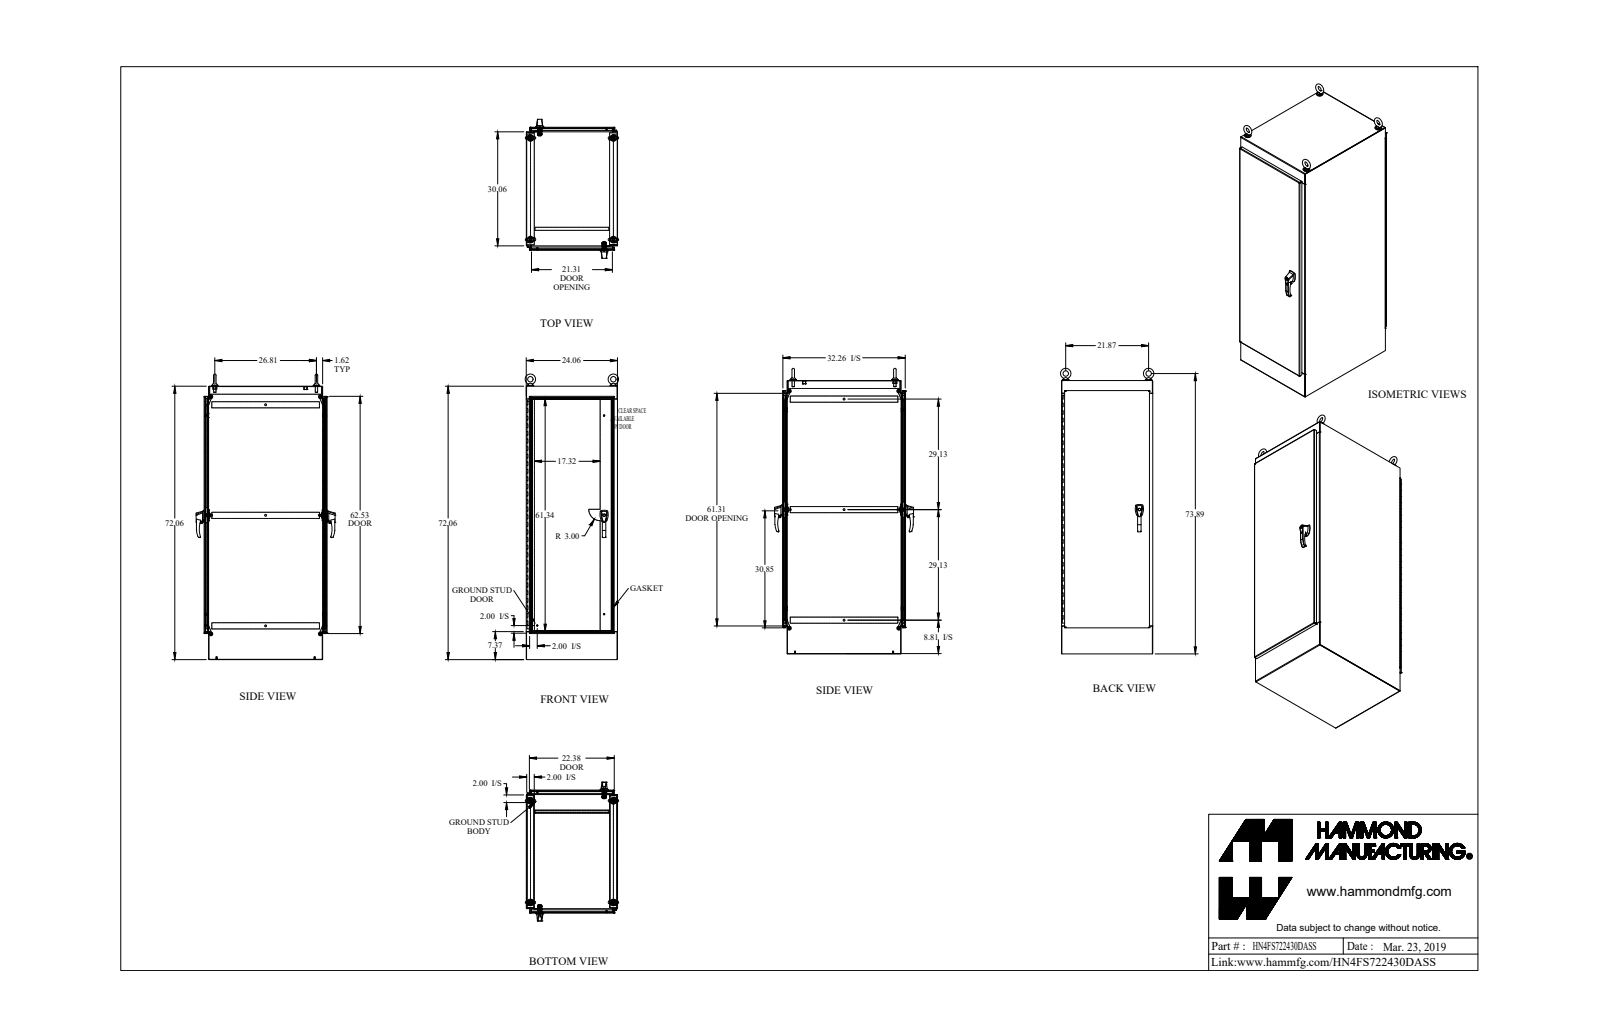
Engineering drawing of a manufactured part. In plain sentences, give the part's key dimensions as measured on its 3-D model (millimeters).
The part is named "HN4FS722430DASS". Its 3-D file was written by "SolidWorks 2018 (AUTOMOTIVE_DESIGN)". It is 90 solids with 3280 faces: 1437 planar, 1515 cylindrical and 328 other. Overall it measures 1911.5 by 931.3 by 624.9 millimeters. Its volume is 19 210 000 cubic millimeters and its surface area 15 830 000 square millimeters. Round holes: 20 of diameter 7.7, 8 of diameter 8.9, 4 of diameter 6.4, 4 of diameter 6.5, 4 of diameter 7.1, 4 of diameter 7.1, 4 of diameter 8, 4 of diameter 9.9, 4 of diameter 10.5, 4 of diameter 15.9, 4 of diameter 17.3, 4 of diameter 19.1. Round bosses or shafts: 4 of diameter 44.5, 4 of diameter 38.1, 4 of diameter 31.8, 4 of diameter 25.4, 4 of diameter 19.1, 4 of diameter 18.7, 4 of diameter 16, 4 of diameter 11.2. Partial cylindrical surfaces (rounded edges, fillets, slot ends): 44 of radius 3.2, 42 of radius 1.1, 36 of radius 3.5, 32 of radius 0.4, 26 of radius 1.2, 26 of radius 3.6, 26 of radius 12.7, 21 of radius 1.5. The main face-to-face distances are 2.4, 608.7, 821.4, 606.3, 611.1, 30.1, 791.3, 819, 1827.9, 823.8. The hole center spacings are 152.4, 587.2, 304.8, 643.9, 457.2, 728.5, 609.6, 832.6.
